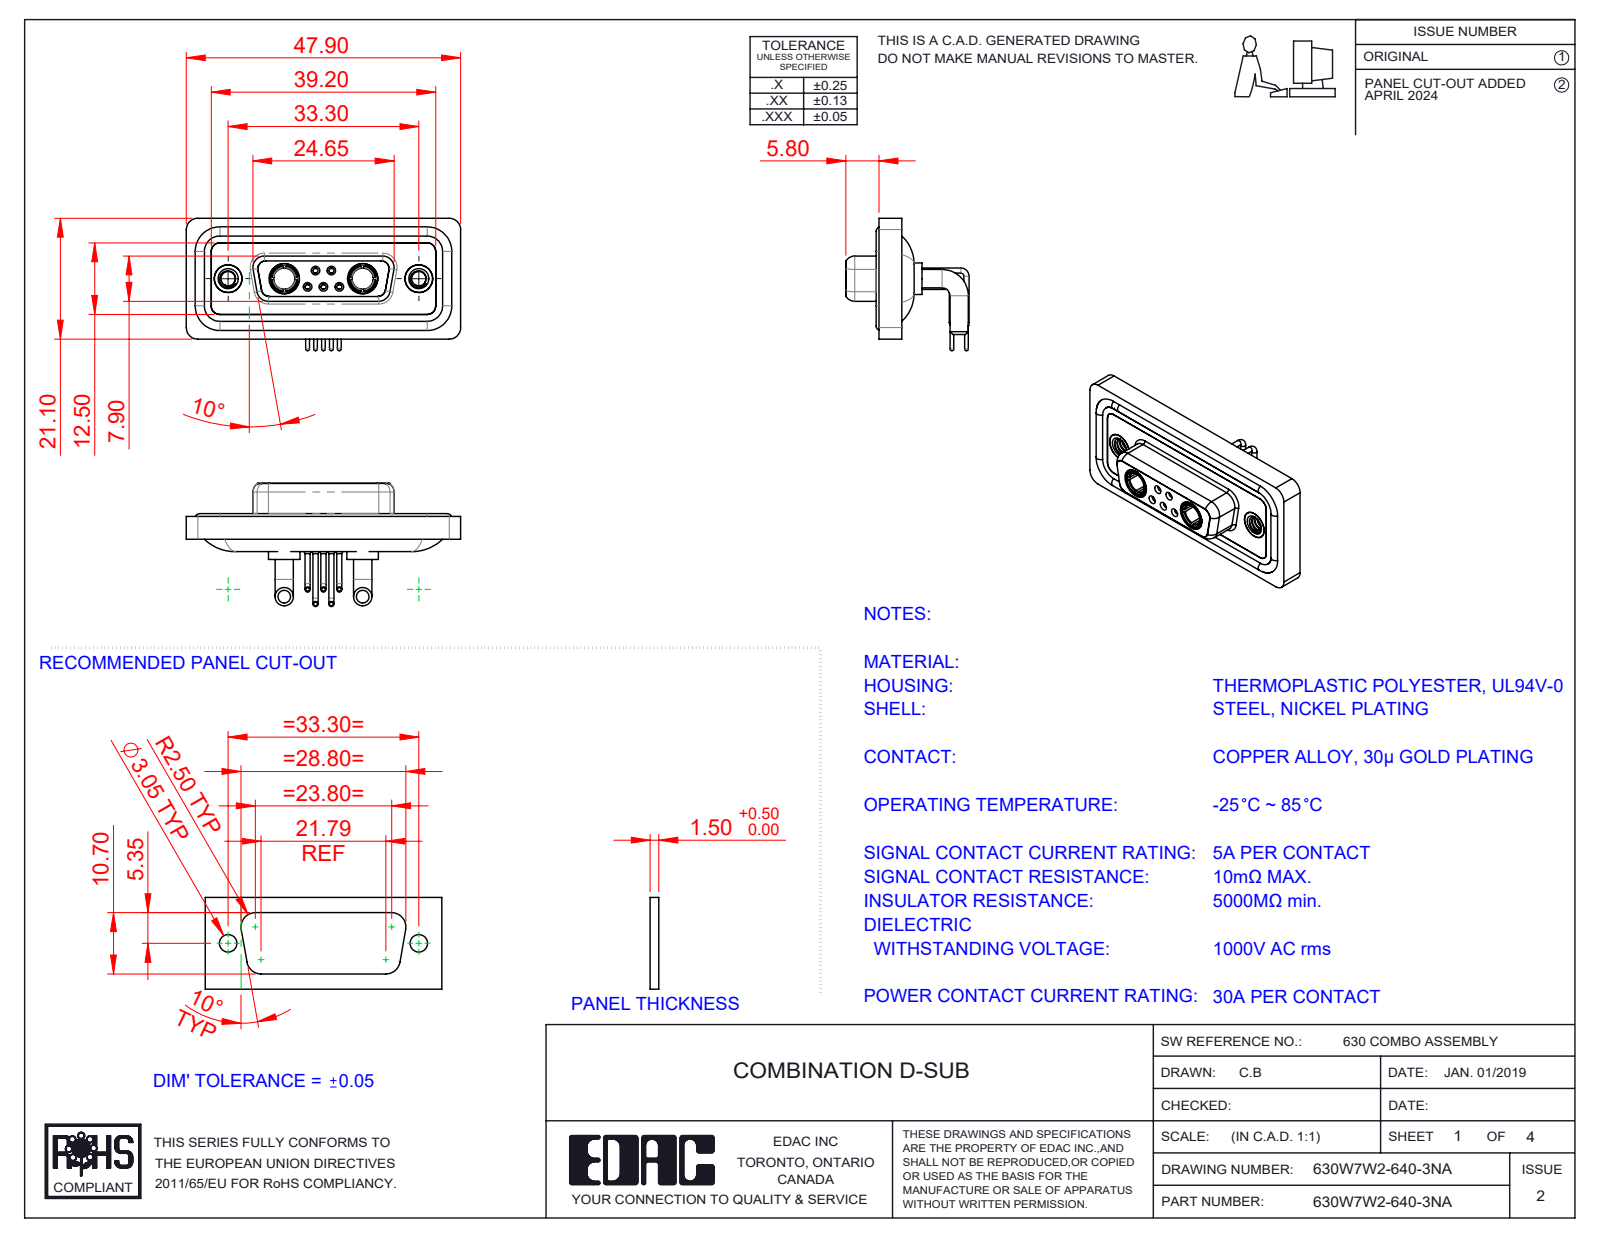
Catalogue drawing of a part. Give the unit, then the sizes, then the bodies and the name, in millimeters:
Units: millimetres
Overall size (bounding box): 47.9 × 23.12 × 21.53
Round holes (diameter × count): ⌀0.9 ×5, ⌀1.1 ×5, ⌀1.5 ×5, ⌀2 ×5, ⌀4.85 ×4, ⌀1.6 ×3, ⌀1.7 ×2, ⌀2.5 ×2, ⌀3.7 ×2, ⌀4 ×2, ⌀4.05 ×2, ⌀5 ×2
Round bosses / shafts (diameter × count): ⌀1.6 ×6, ⌀0.9 ×5, ⌀0.65 ×5, ⌀3.2 ×4, ⌀5.5 ×2, ⌀5.2 ×2, ⌀4.96 ×2, ⌀4.95 ×2
Partial cylindrical surfaces — rounded edges, fillets, slot ends (radius × count): R2 ×20, R1.5 ×18, R1.35 ×12, R1.6 ×8, R0.25 ×4, R0.5 ×4, R0.6 ×4, R0.65 ×4
Main face-to-face distances: 0.4, 1.8, 1.1, 1.6, 2.9, 2.5, 3.1, 3.7, 4.1, 1.5
Hole centre spacings: 3.16, 2.77, 9.8, 23.5, 4.31, 4.33, 5.03, 5.04
Volume: 6 245 mm³ · Surface area: 10 245 mm²
Bodies: 16 solids, 801 faces (238 planar, 351 cylindrical, 212 other)
Part name (STEP PRODUCT): 630Combo Contact Row 1_50 Contacts; 630W7W2-640-3NA; 630Combo Waterproof Housing_15 Contacts; 630Combo Housing_7W2 (+5 more)
STEP written by: SolidWorks 2023 (CONFIG_CONTROL_DESIGN)
